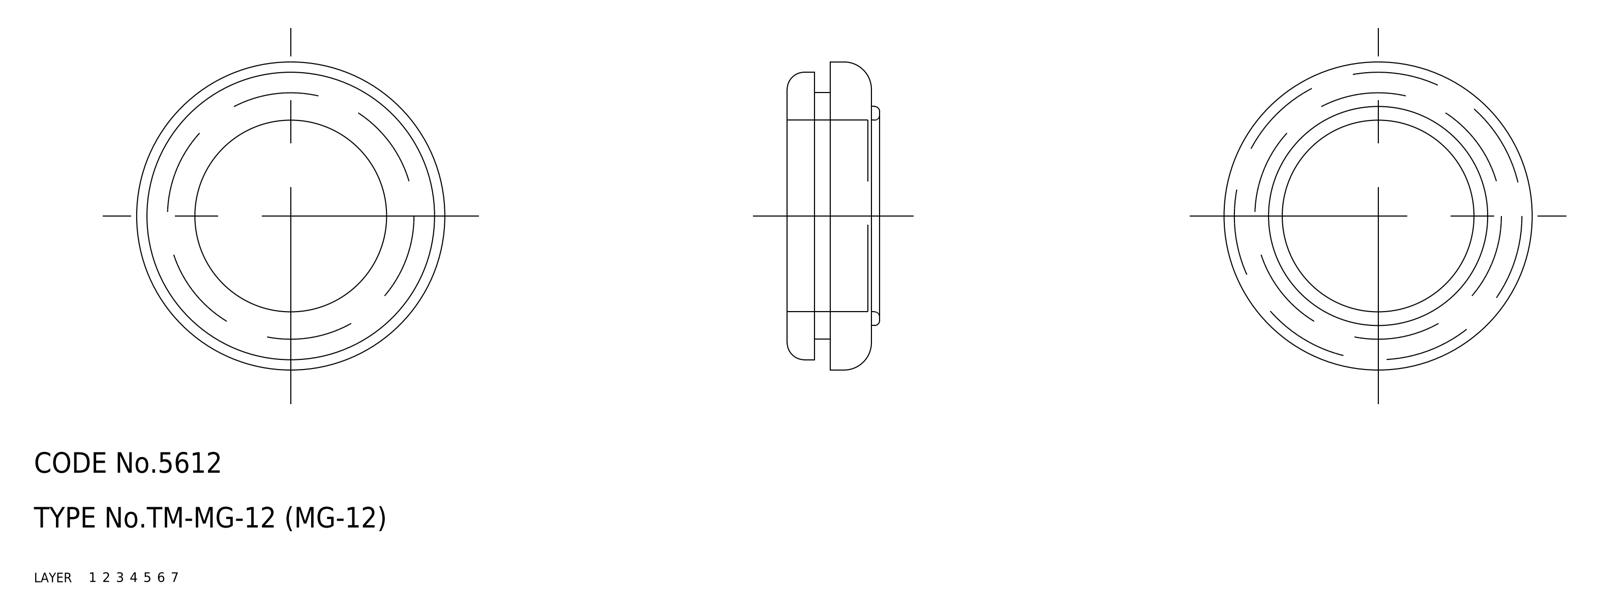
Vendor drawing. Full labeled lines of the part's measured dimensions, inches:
Part name (STEP PRODUCT): 67110919
STEP written by: CADfix (AUTOMOTIVE_DESIGN)
Units: inches
Bodies: 1 solid, 27 faces (0 planar, 0 cylindrical, 27 other)
Overall size (bounding box): 1.772 × 1.772 × 0.531
Volume: 0.595 in³ · Surface area: 9.866 in²
